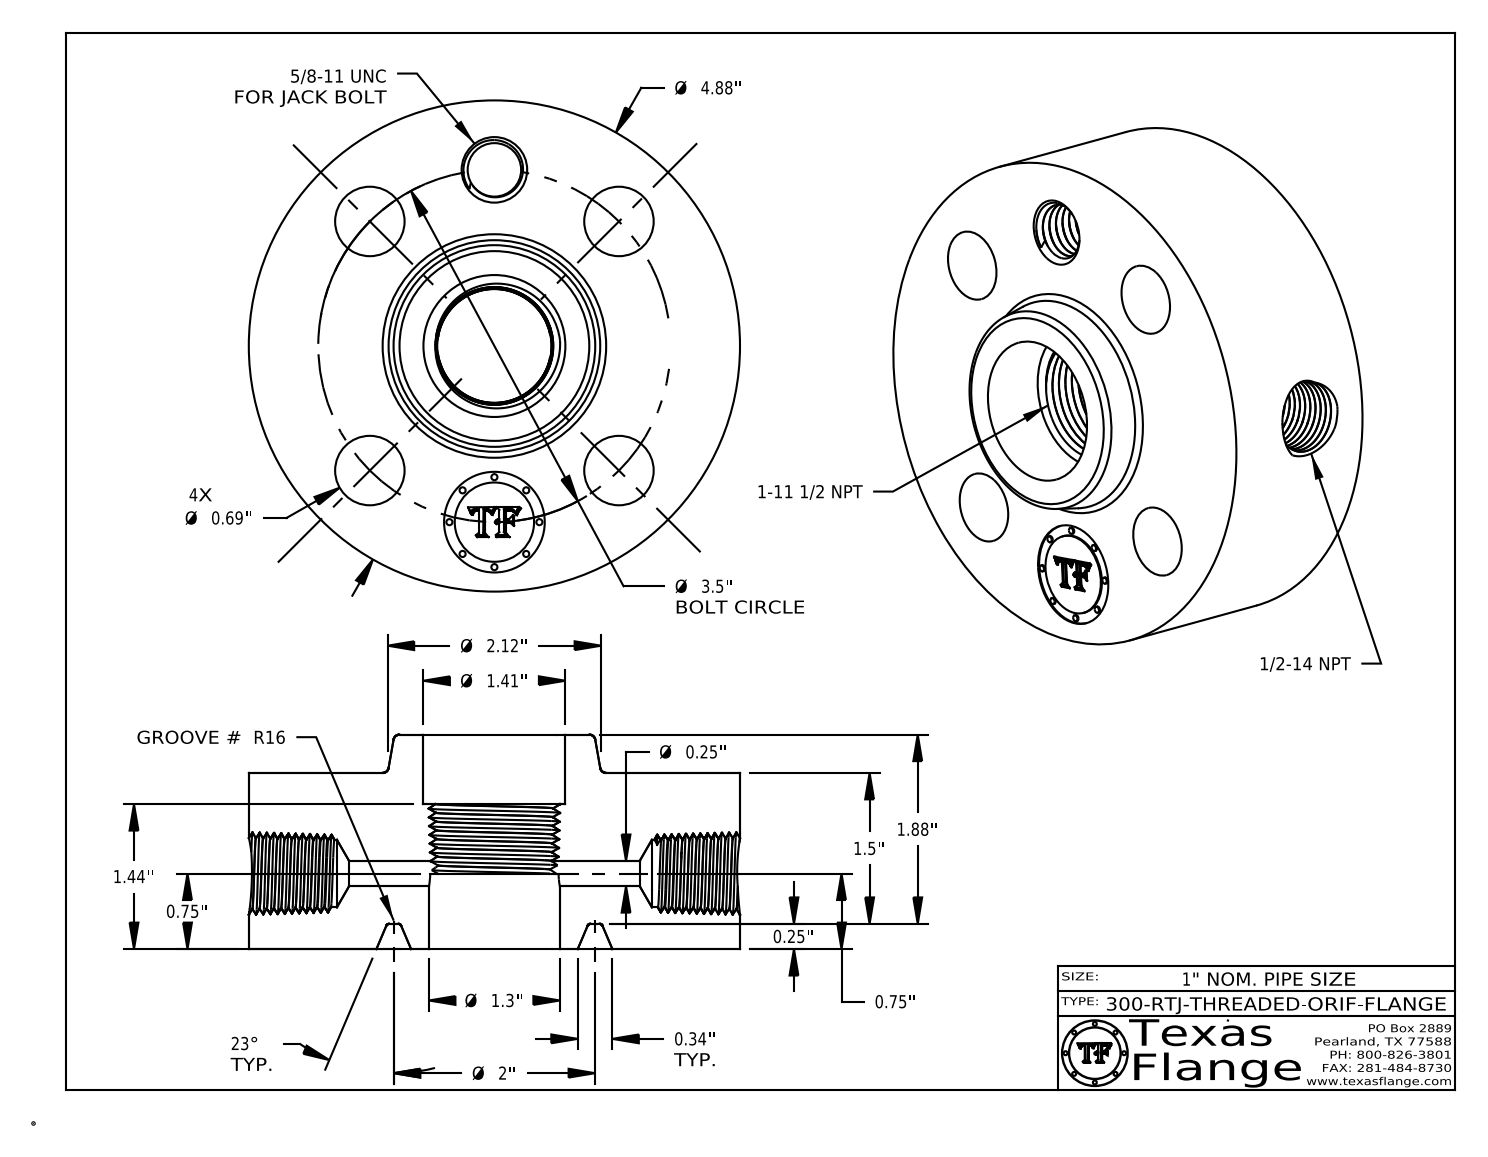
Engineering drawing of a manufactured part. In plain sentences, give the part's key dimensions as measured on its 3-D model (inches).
The part is named "300-RTJ-THREADED". Its 3-D file was written by "CATIA V5 STEP AP214 (AUTOMOTIVE_DESIGN)". It is 1 solid with 879 faces: 373 planar, 91 cylindrical and 415 other. Overall it measures 4.88 by 4.88 by 2.13 inches. Its volume is 26.8 cubic inches and its surface area 101.2 square inches. Round holes: 4 of diameter 0.69, 1 of diameter 0.25, 1 of diameter 0.531, 1 of diameter 0.672, 1 of diameter 1, 1 of diameter 1.3, 1 of diameter 1.41. Round bosses or shafts: 8 of diameter 0.061, 1 of diameter 4.88, 1 of diameter 0.788. The main face-to-face distances are 1.75, 2.13, 0.38, 0.25, 1.5, 1.88, 1.44, 1.19, 0.31, 0.69. The hole center spacings are 1.75, 1.339, 2.475, 3.233, 3.5.
